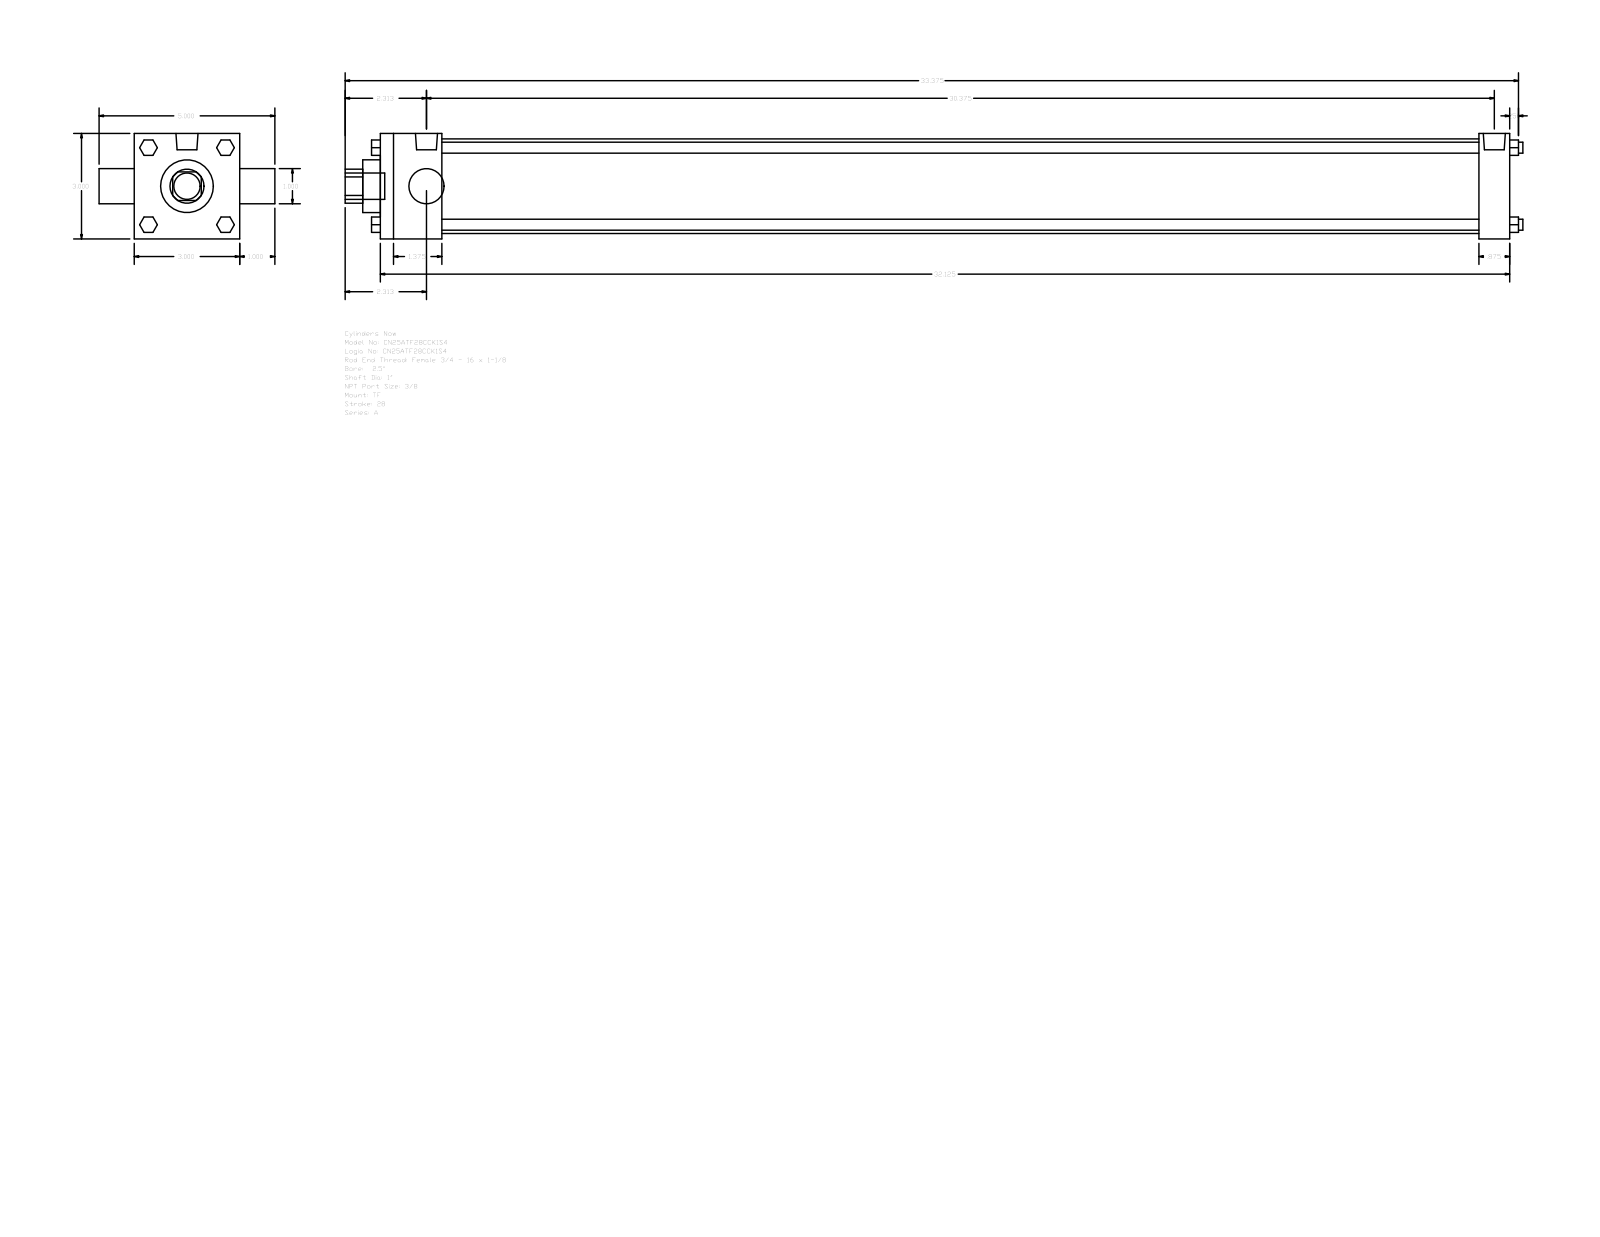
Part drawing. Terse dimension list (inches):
name: A_TF__0250_1
written by: GSSL Pune (CONFIG_CONTROL_DESIGN)
unit: in
bodies: 0 solids, 120 faces (92 planar, 28 cylindrical, 0 other)
size: 33.5 × 5 × 3
holes: 2× ⌀1, 1× ⌀1.5, 1× ⌀2.69
bosses: 4× ⌀0.313, 3× ⌀0.219, 2× ⌀0.627, 1× ⌀0.75
rounds: 1× R0.484
face distances: 3, 32.125, 1.75, 31.25, 29.5, 30.375, 0.875, 1, 4, 32.625
